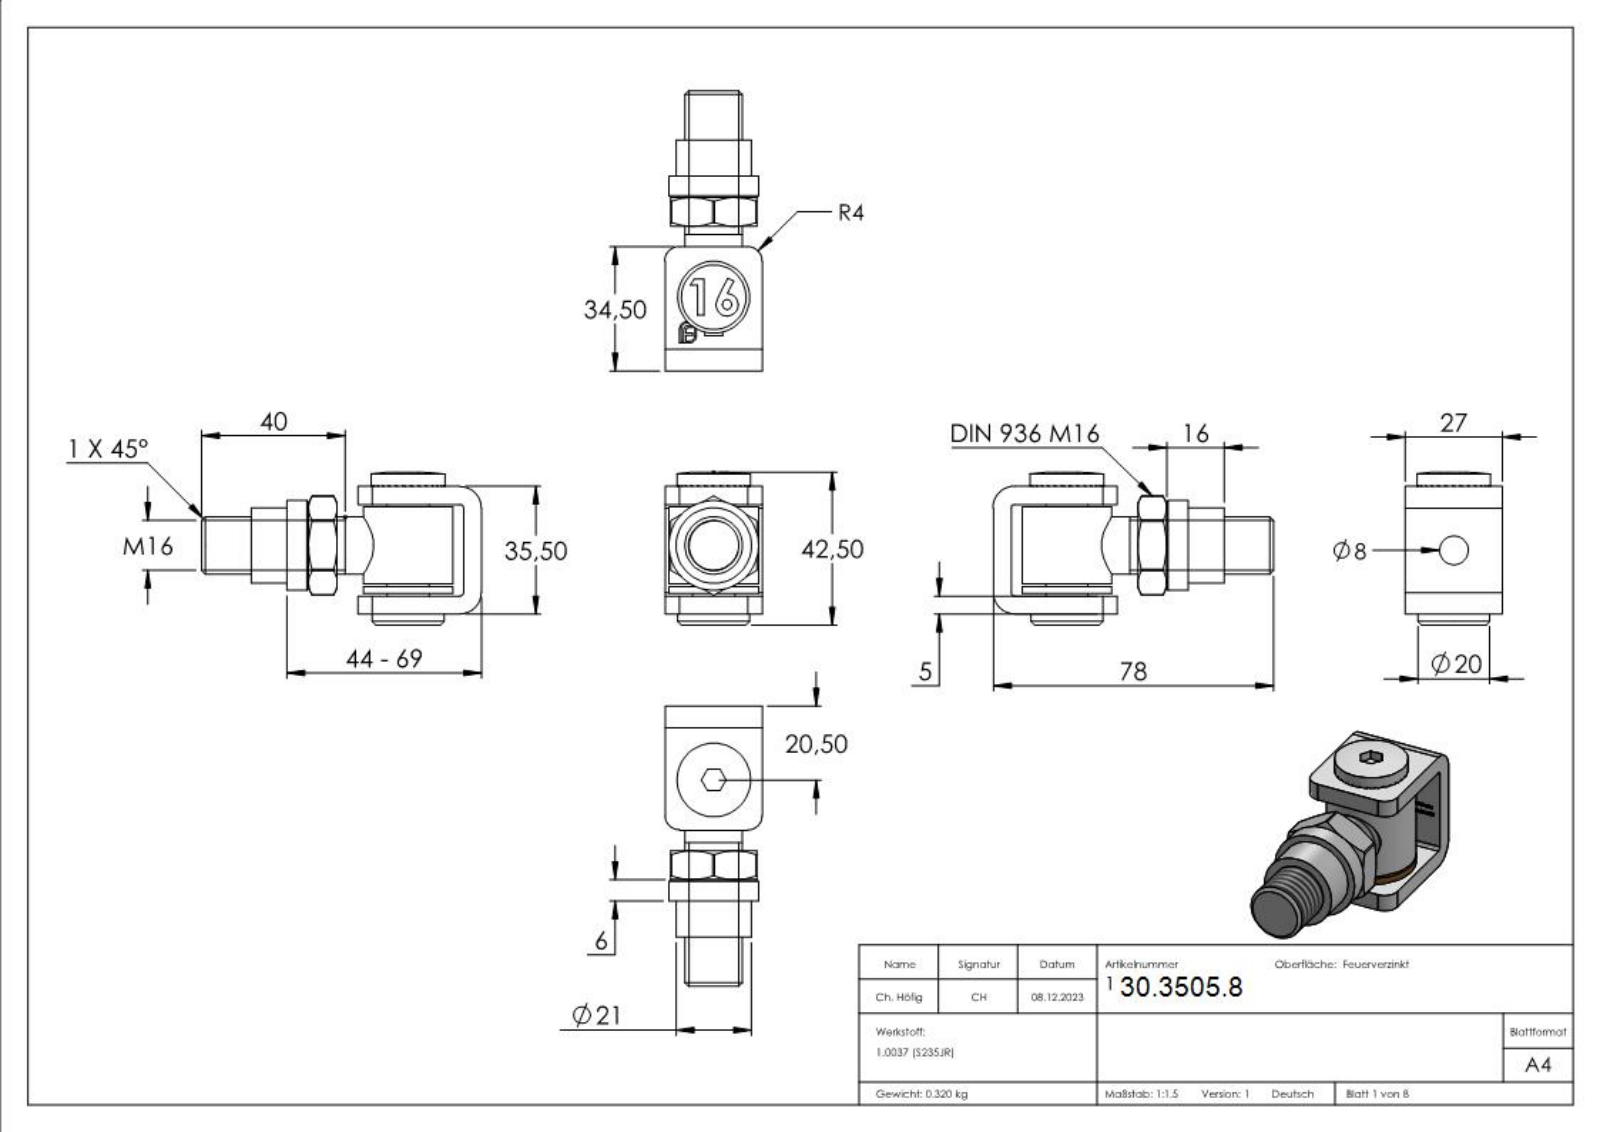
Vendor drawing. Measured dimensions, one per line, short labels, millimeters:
name: 120-M16-FEV; Torband Teil5_120-M16-FEV Teil5; DIN 936 M8-M24_DIN 936 M16; Torband Teil2_120-M16-FEV Teil2 (+4 more)
written by: SolidWorks 2018 (CONFIG_CONTROL_DESIGN)
unit: mm
bodies: 7 solids, 517 faces (342 planar, 31 cylindrical, 144 other)
size: 78 × 42.46 × 27
volume: 40 965 mm³; area: 20 348 mm²
holes: 1× ⌀5, 1× ⌀8, 1× ⌀12.5, 1× ⌀14
bosses: 2× ⌀25, 1× ⌀21, 1× ⌀20.5, 1× ⌀20, 1× ⌀16, 1× ⌀11.8, 1× ⌀6
rounds: 6× R0.5, 2× R1, 2× R4, 2× R6
face distances: 5, 30.5, 25.5, 35.5, 5.67, 29.83, 0.67, 24.83, 48.25, 43.25
hole spacings: 1.33
